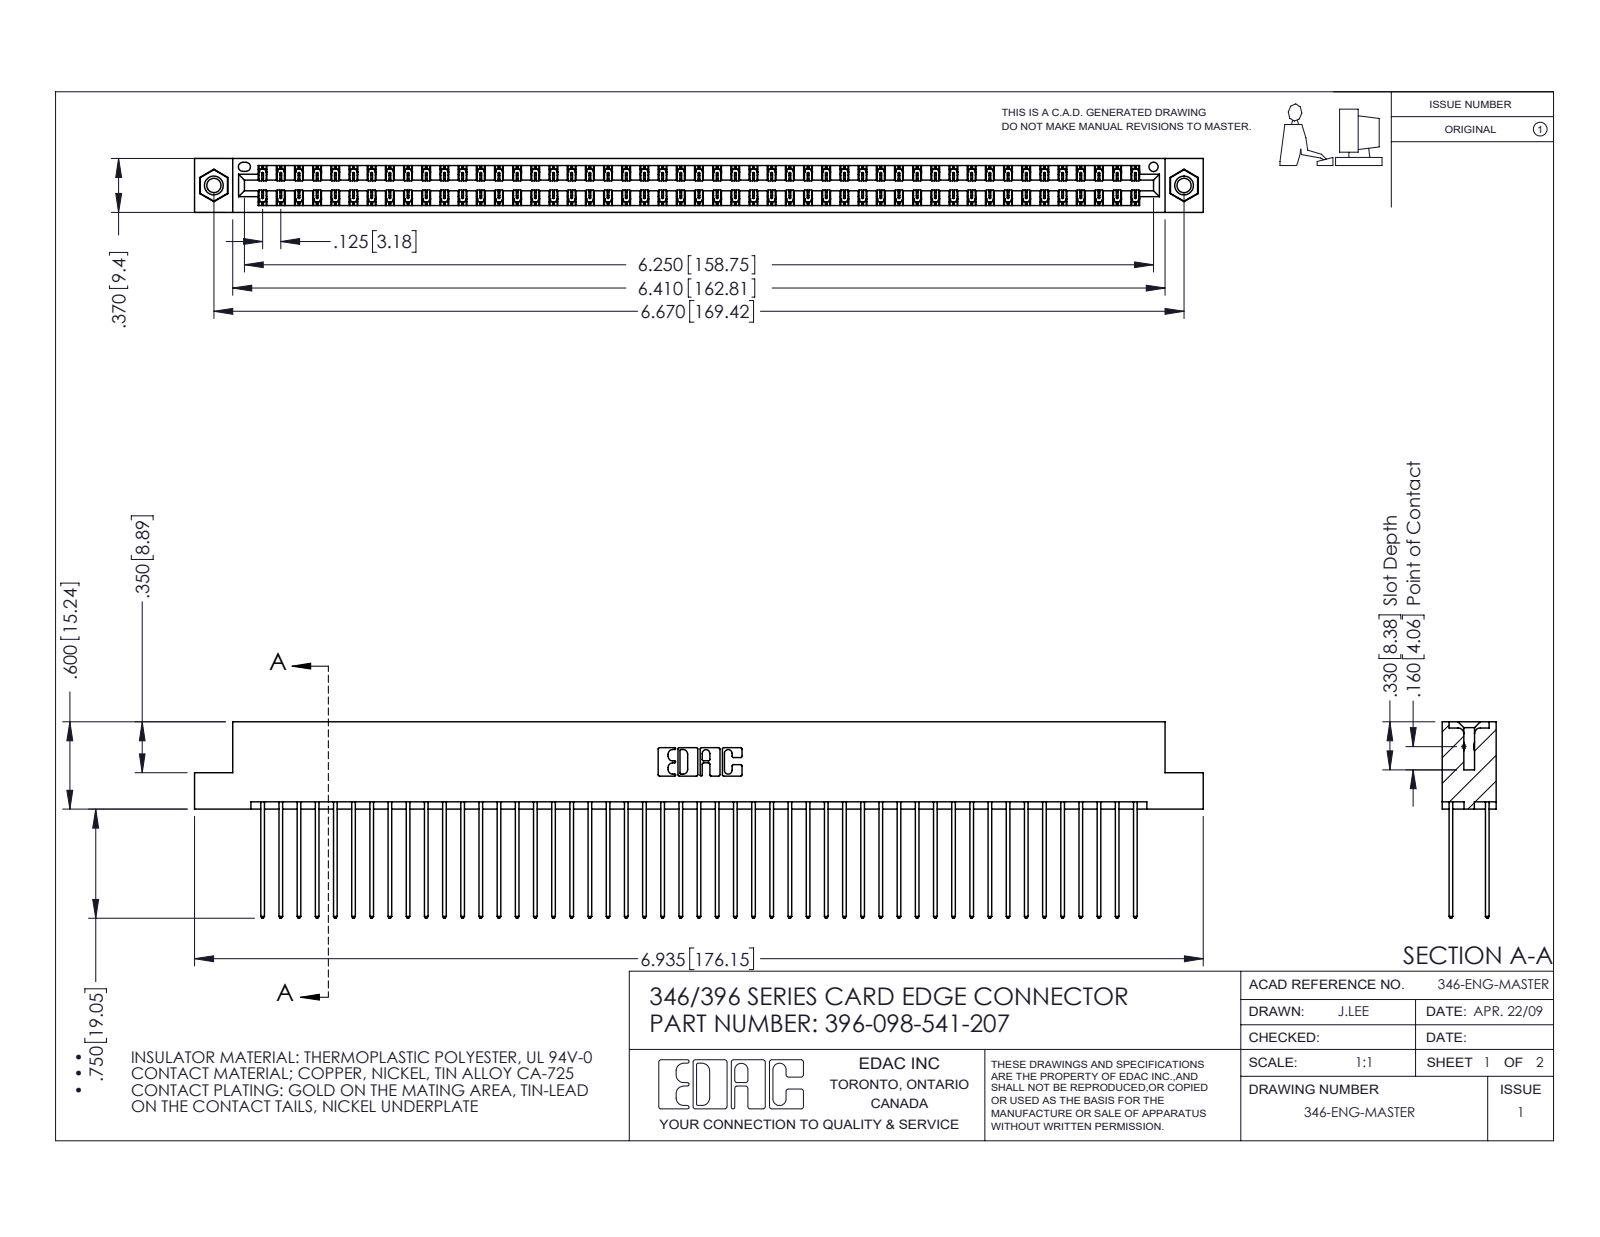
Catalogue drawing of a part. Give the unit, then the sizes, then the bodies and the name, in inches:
Units: inches
Overall size (bounding box): 6.935 × 1.35 × 0.37
Round holes (diameter × count): ⌀0.098 ×2, ⌀0.125 ×2, ⌀0.156 ×2, ⌀0.064 ×1
Round bosses / shafts (diameter × count): ⌀0.155 ×2
Partial cylindrical surfaces — rounded edges, fillets, slot ends (radius × count): R0.006 ×147, R0.01 ×98, R0.01 ×22, R0.007 ×6, R0.031 ×6, R0.026 ×3, R0.014 ×2, R0.022 ×2
Main face-to-face distances: 0.048, 0.322, 0.25, 0.072, 0.298, 0.025, 0.37, 0.275, 0.225, 0.148
Hole centre spacings: 0.246, 6.461, 6.67
Volume: 1.085 in³ · Surface area: 42.28 in²
Bodies: 101 solids, 5278 faces (3538 planar, 1724 cylindrical, 16 other)
Part name (STEP PRODUCT): 345-292-001_345-293-141; 345-250-001_345-250-005-103; 396-098-541-207; 346 Part_Flush Mounting Lugs - 0.156 Dia-TI
STEP written by: SolidWorks 2016 (CONFIG_CONTROL_DESIGN)
